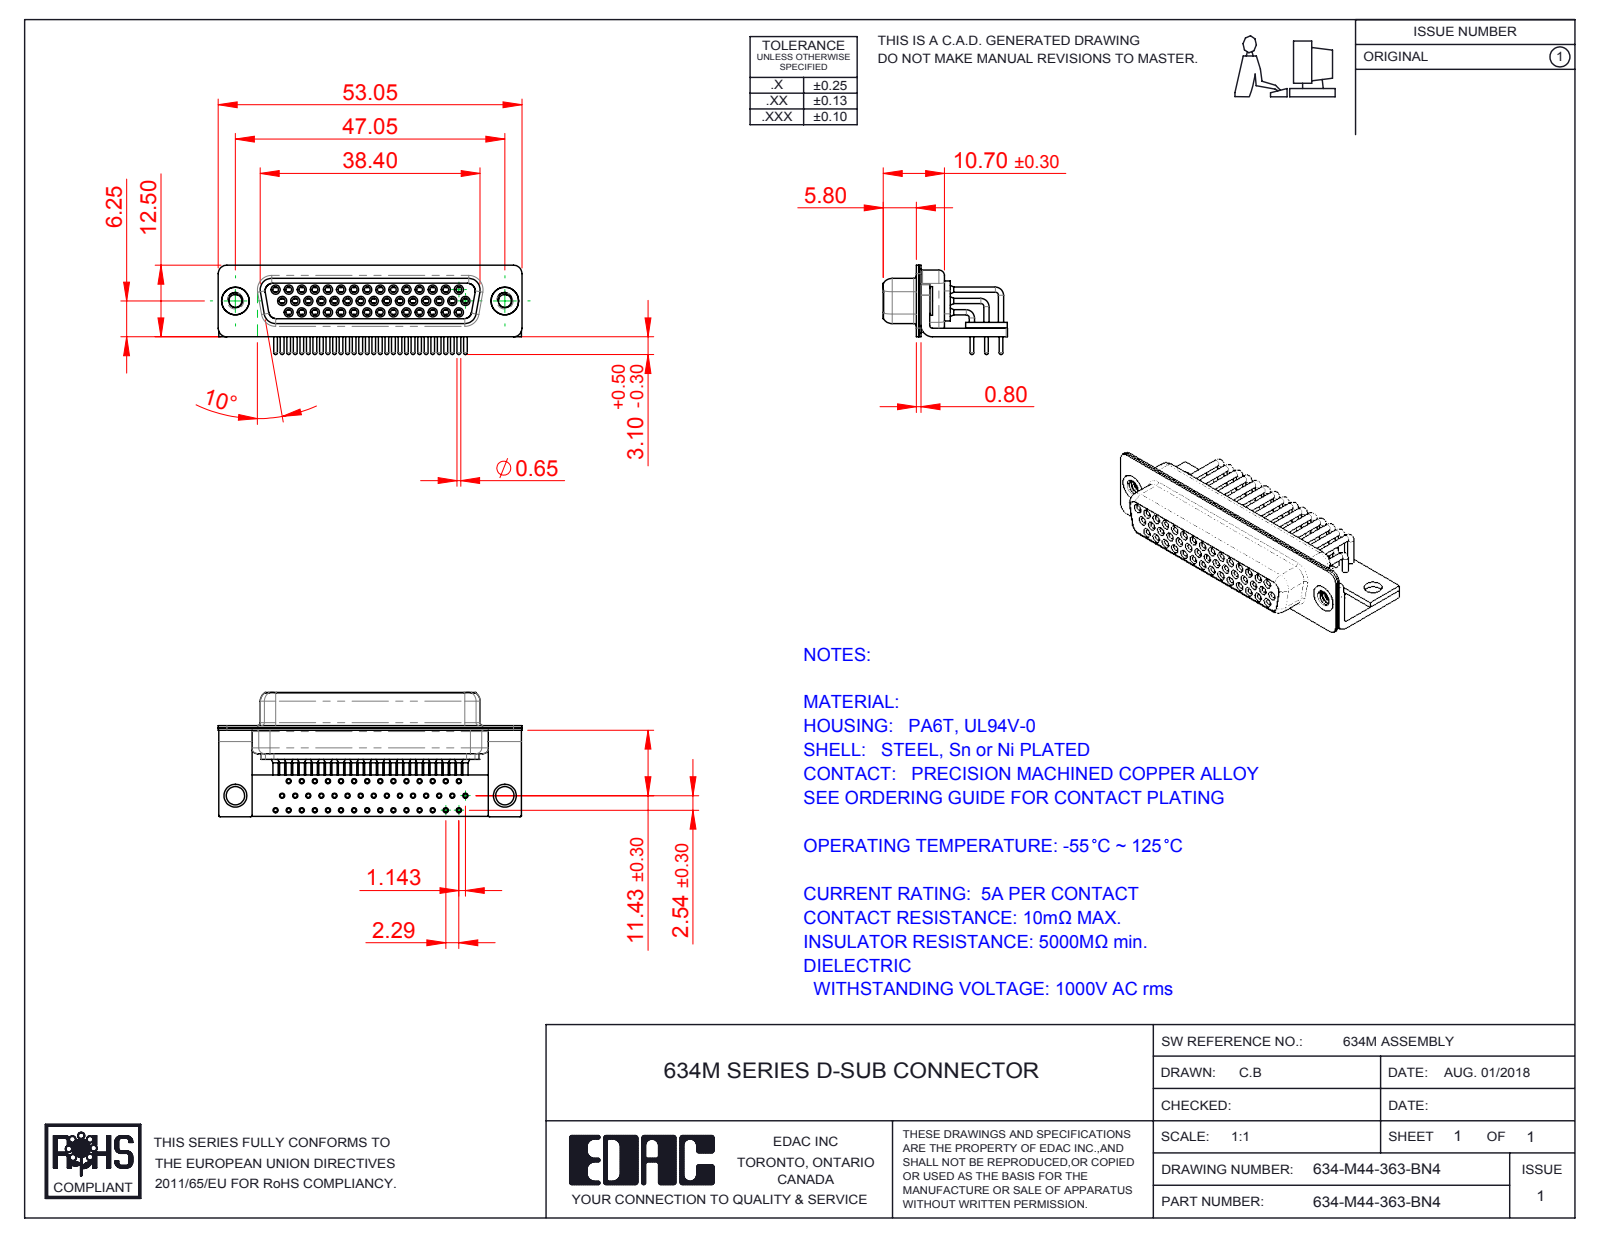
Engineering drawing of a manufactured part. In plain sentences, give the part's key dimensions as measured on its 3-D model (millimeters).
The part is named "634M Shell Front_44 Contacts; 634M Stabilizer Board_44 Contacts; 634M Shell Rear_44 Contacts; 634M Contact Row 1 (+6 more)". Its 3-D file was written by "SolidWorks 2016 (CONFIG_CONTROL_DESIGN)". It is 52 solids with 2749 faces: 753 planar, 1259 cylindrical and 737 other. Overall it measures 53.05 by 21.7 by 15.6 millimeters. Its volume is 4 457 cubic millimeters and its surface area 14 593 square millimeters. Round holes: 44 of diameter 0.9, 44 of diameter 1, 44 of diameter 1.1, 44 of diameter 1.7, 44 of diameter 1.8, 44 of diameter 2, 2 of diameter 2.26, 2 of diameter 3.2, 2 of diameter 4, 2 of diameter 4.8. Round bosses or shafts: 44 of diameter 1.6, 44 of diameter 1.5, 44 of diameter 0.9, 44 of diameter 0.65, 2 of diameter 5, 2 of diameter 4.9. Partial cylindrical surfaces (rounded edges, fillets, slot ends): 16 of radius 0.25, 16 of radius 1.5, 13 of radius 2, 8 of radius 1.35, 8 of radius 1.6, 5 of radius 0.5, 4 of radius 0.6, 4 of radius 0.65. The main face-to-face distances are 0.4, 2.3, 1, 1.9, 0.8, 9.35, 1.45, 8.95, 0.85, 8.5. The hole center spacings are 2.28, 2.29, 4.57, 6.86, 11.43, 3.96, 8.24, 9.14.
